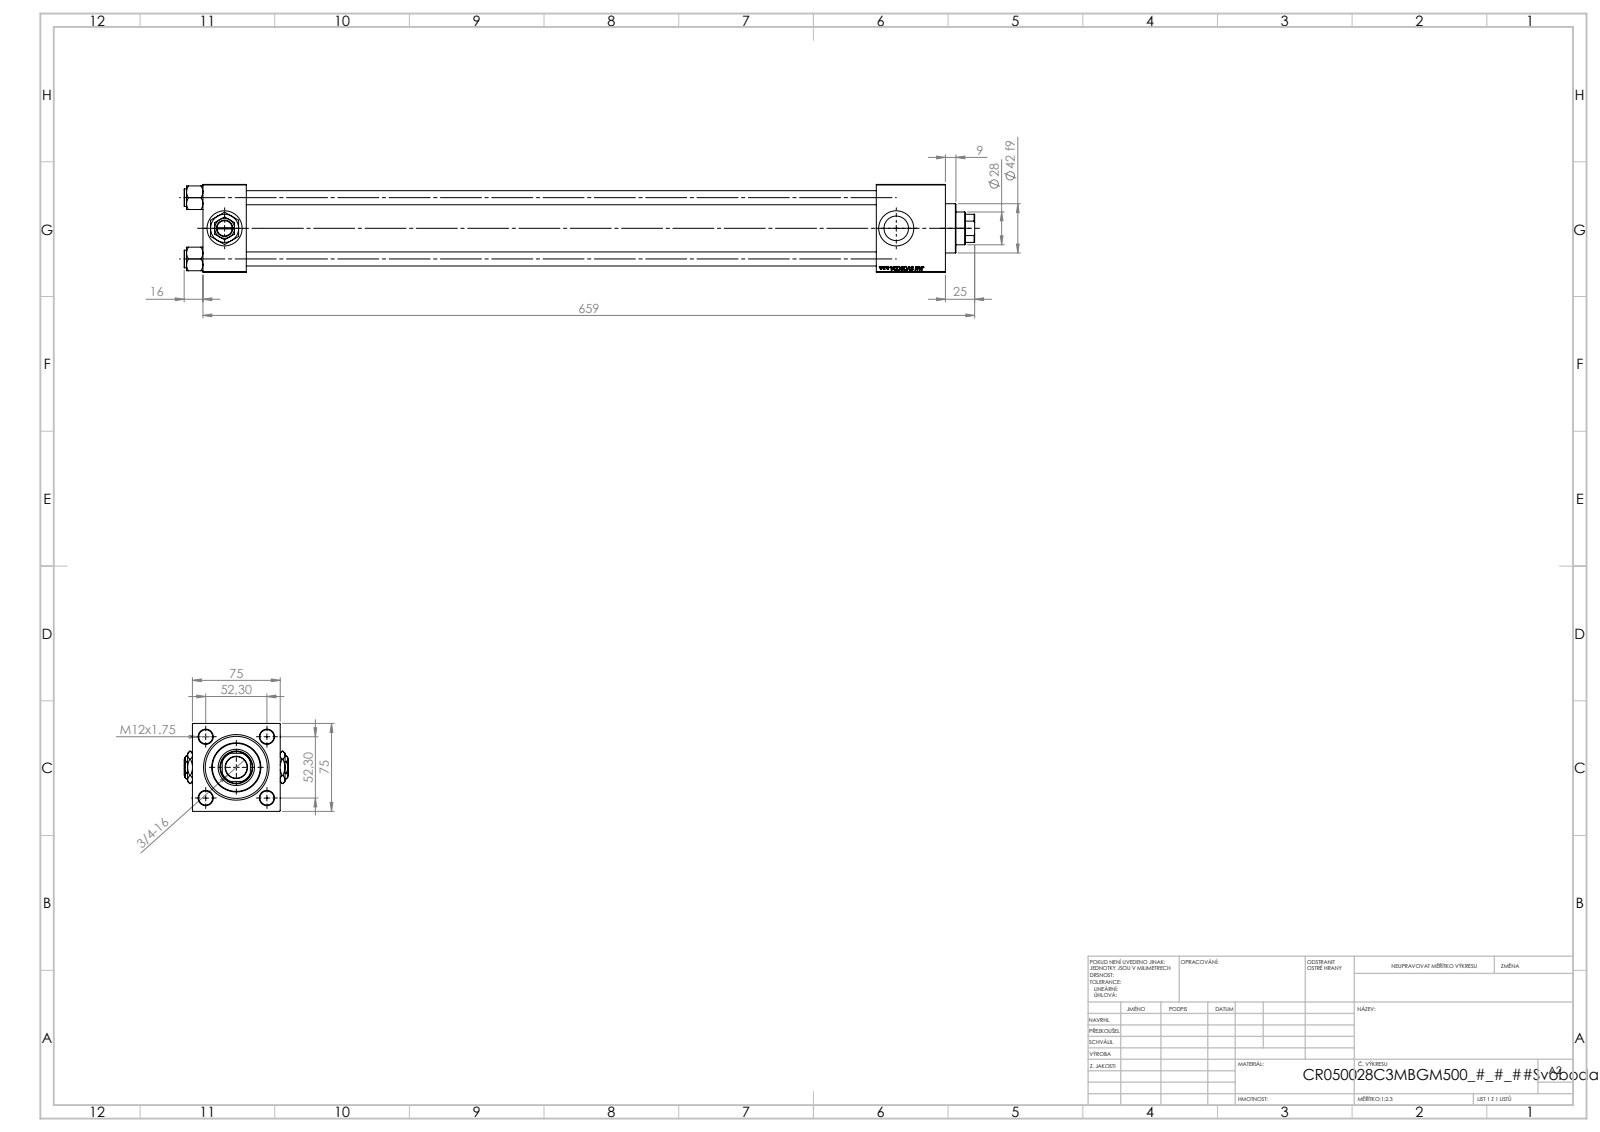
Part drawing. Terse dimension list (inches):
name: NUT_M5_C; V215CR_C_Body; Zatka_pro_OIL_PORT; V215CR_VCP_C (+2 more)
written by: SolidWorks 2019 (CONFIG_CONTROL_DESIGN)
unit: in
bodies: 13 solids, 1249 faces (573 planar, 98 cylindrical, 578 other)
size: 26.575 × 3.504 × 2.953
volume: 86.41 in³; area: 666.3 in²
holes: 4× ⌀0.472, 2× ⌀0.276, 2× ⌀0.825, 2× ⌀1.181, 1× ⌀0.728, 1× ⌀1.102, 1× ⌀1.22, 1× ⌀1.614, 1× ⌀1.969, 1× ⌀2.087
bosses: 4× ⌀0.591, 1× ⌀2.205, 1× ⌀1.654
rounds: 1× R0.531
face distances: 2.953, 1.457, 24.961, 23.504, 22.638, 21.181, 2.323, 23.831, 22.374, 1.193
hole spacings: 1.456, 2.059, 2.912, 22.579
